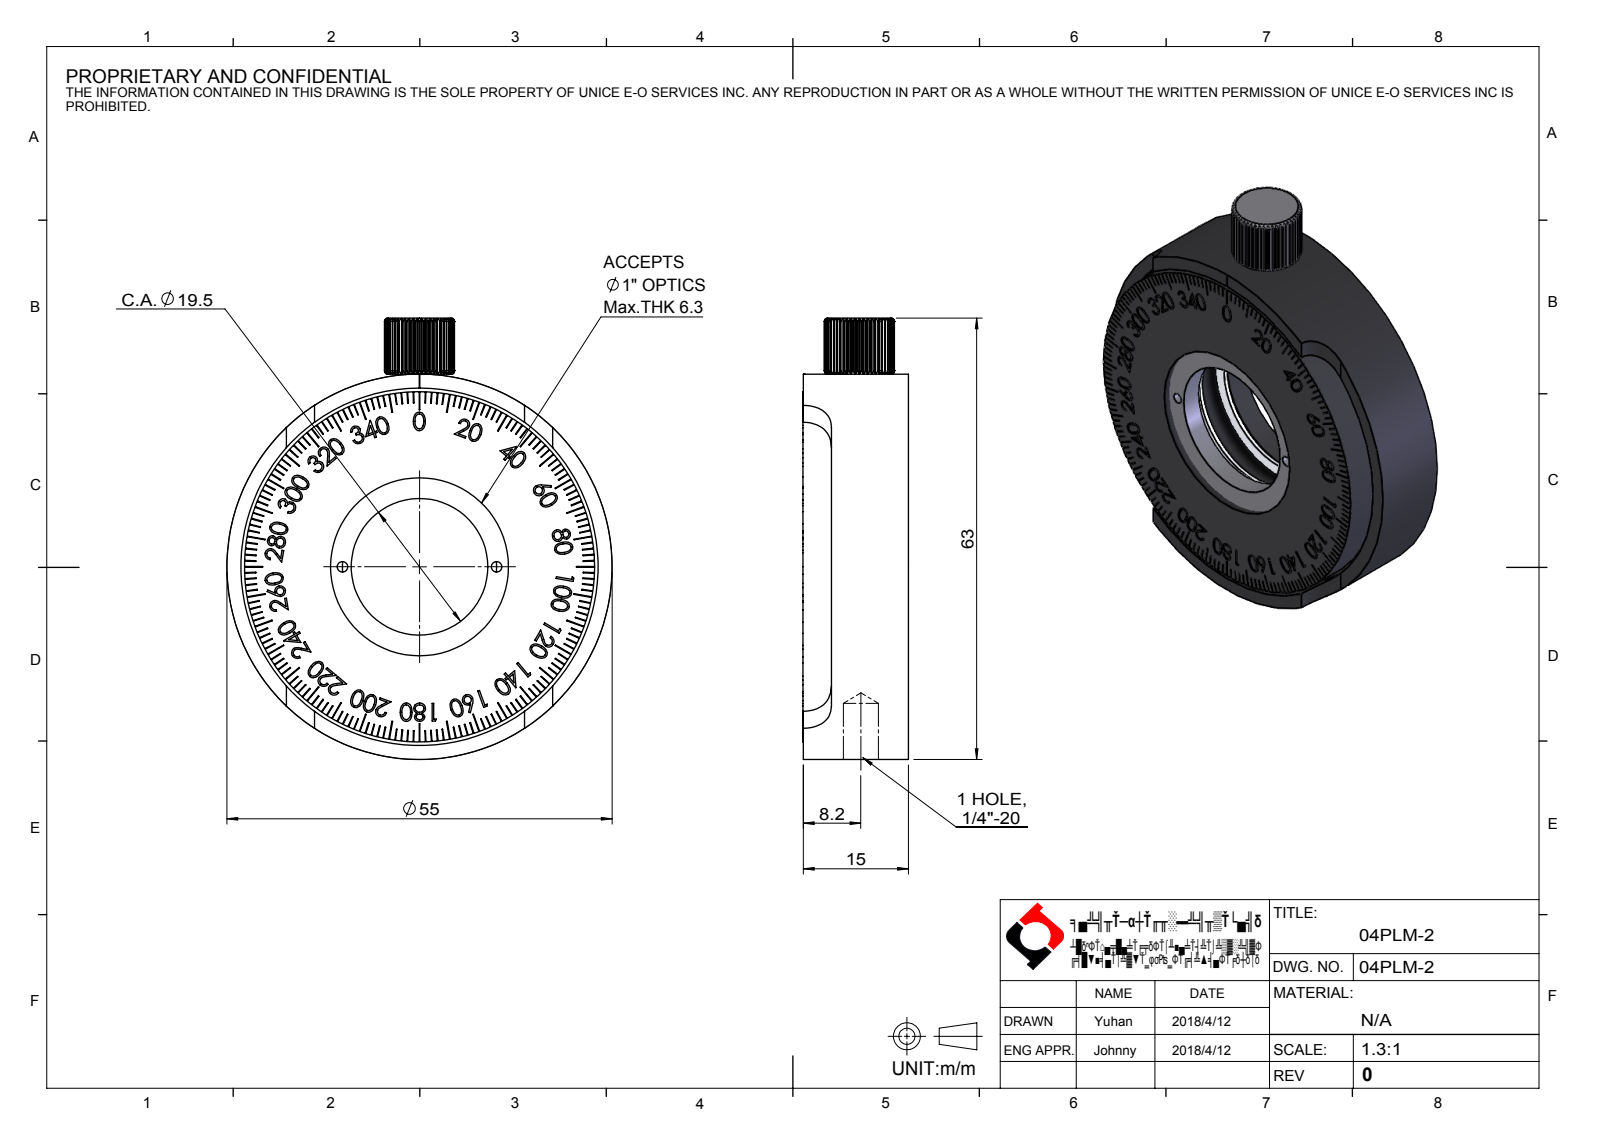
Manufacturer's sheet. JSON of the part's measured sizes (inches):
{"part_name": "04PLM-2", "step_written_by": "SolidWorks 2016 (CONFIG_CONTROL_DESIGN)", "units": "inches", "bodies": {"solids": 12, "faces": 1891, "planar": 1309, "cylindrical": 195, "other": 387}, "overall_size": [2.48, 2.165, 0.593], "volume_in3": 1.717, "surface_area_in2": 30.44, "round_holes": [[0.098, 4], [0.134, 4], [0.256, 4], [0.059, 2], [0.13, 1], [0.768, 1], [0.866, 1], [0.906, 1], [1, 1], [1.378, 1], [2.008, 1]], "round_bosses_or_shafts": [[0.217, 4], [0.118, 4], [2.165, 1], [1.969, 1], [1.035, 1], [1.004, 1], [0.157, 1]], "partial_cylinders_radius": [[0.157, 2], [0.197, 1]], "face_to_face_distances": [0.254, 0.197, 0.591, 0.394, 0.138, 0.14, 0.453, 0.252, 0.451, 0.392], "hole_center_spacings": [0.591, 0.732, 0.835, 0.157, 0.433, 1.024, 1.181, 0.866]}
